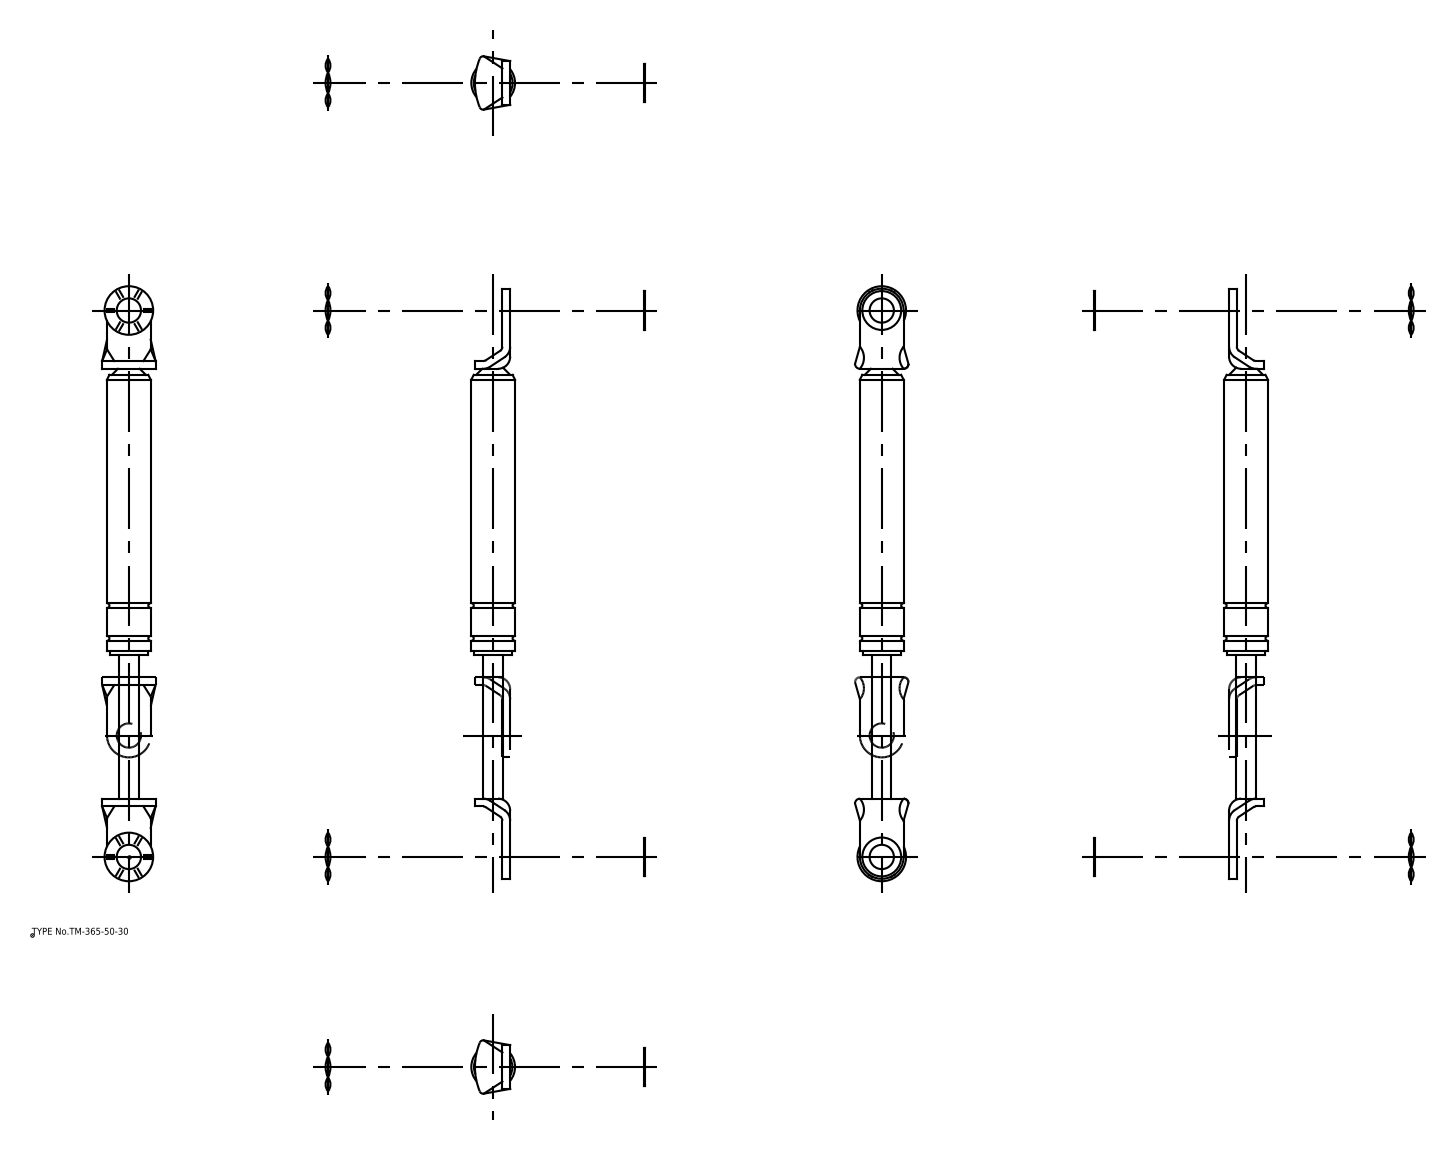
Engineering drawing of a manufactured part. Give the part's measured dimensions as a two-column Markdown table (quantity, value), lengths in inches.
| quantity | value |
| --- | --- |
| part name | ウェーブワッシャー; ワッシャー; 本体; 本体_div |
| STEP written by | spGate 16.7.1 (AUTOMOTIVE_DESIGN) |
| units | inches |
| bodies | 6 solids, 94 faces (42 planar, 44 cylindrical, 8 other) |
| overall size | 9.646 × 0.866 × 0.728 |
| volume | 2.317 in³ |
| surface area | 21.96 in² |
| round holes (diameter × count) | 0.394 × 2 |
| round bosses / shafts (diameter × count) | 0.63 × 3, 0.787 × 2, 0.728 × 1, 0.709 × 1, 0.315 × 1 |
| partial cylindrical surfaces (radius × count) | 0.173 × 2, 0.197 × 2, 0.354 × 2, 1.036 × 1 |
| main face-to-face distances | 0.126, 0.079, 0.205, 7.094, 0.146, 0.224, 0.02, 4.772, 2.449, 7.22 |
| hole center spacings | 8.858 |
